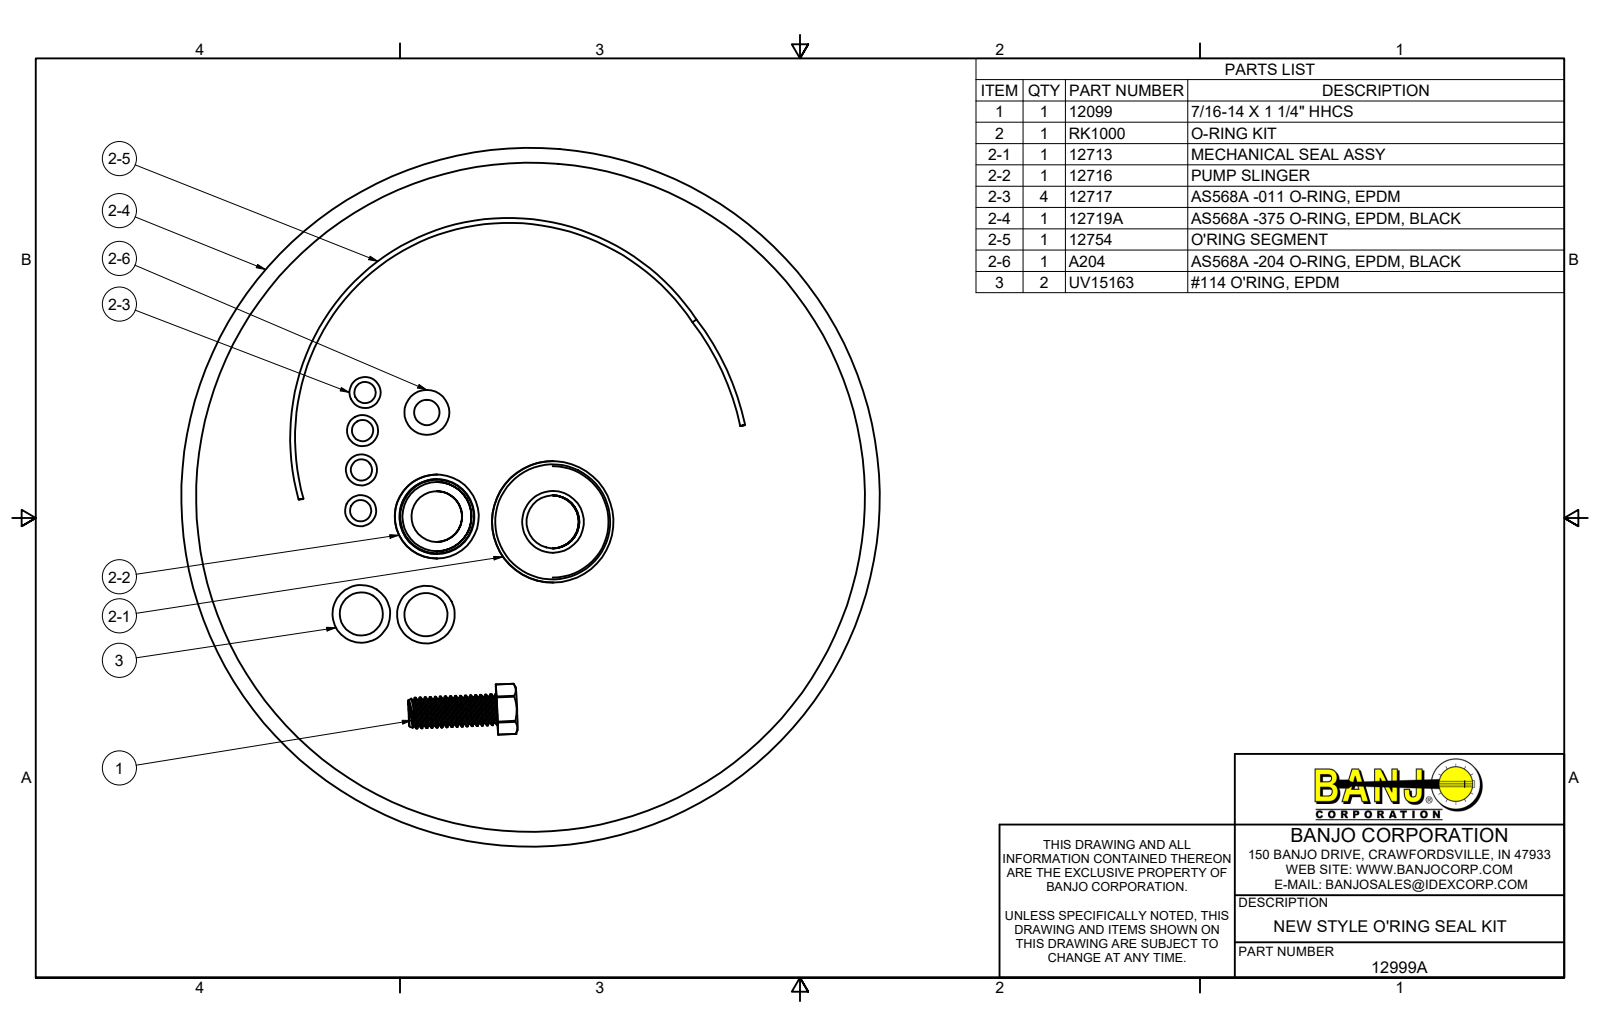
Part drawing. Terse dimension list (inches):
name: 12999A; RK1000; 12716; 12713 (+7 more)
written by: Autodesk Inventor 2019 (AUTOMOTIVE_DESIGN)
unit: in
bodies: 13 solids, 143 faces (26 planar, 59 cylindrical, 58 other)
size: 9.895 × 9.895 × 2.279
volume: 2.686 in³; area: 45.89 in²
holes: 1× ⌀0.719, 1× ⌀0.75, 1× ⌀0.813, 1× ⌀0.875, 1× ⌀0.98, 1× ⌀1
bosses: 17× ⌀0.379, 1× ⌀1.72, 1× ⌀1.575, 1× ⌀1.375, 1× ⌀1.313, 1× ⌀1.305, 1× ⌀1.19, 1× ⌀1.125
rounds: 1× R0.19, 1× R0.356
face distances: 0.38, 0.365, 0.375, 0.031, 0.235, 0.615, 0.406, 0.25, 0.05, 0.641
hole spacings: 1.645
